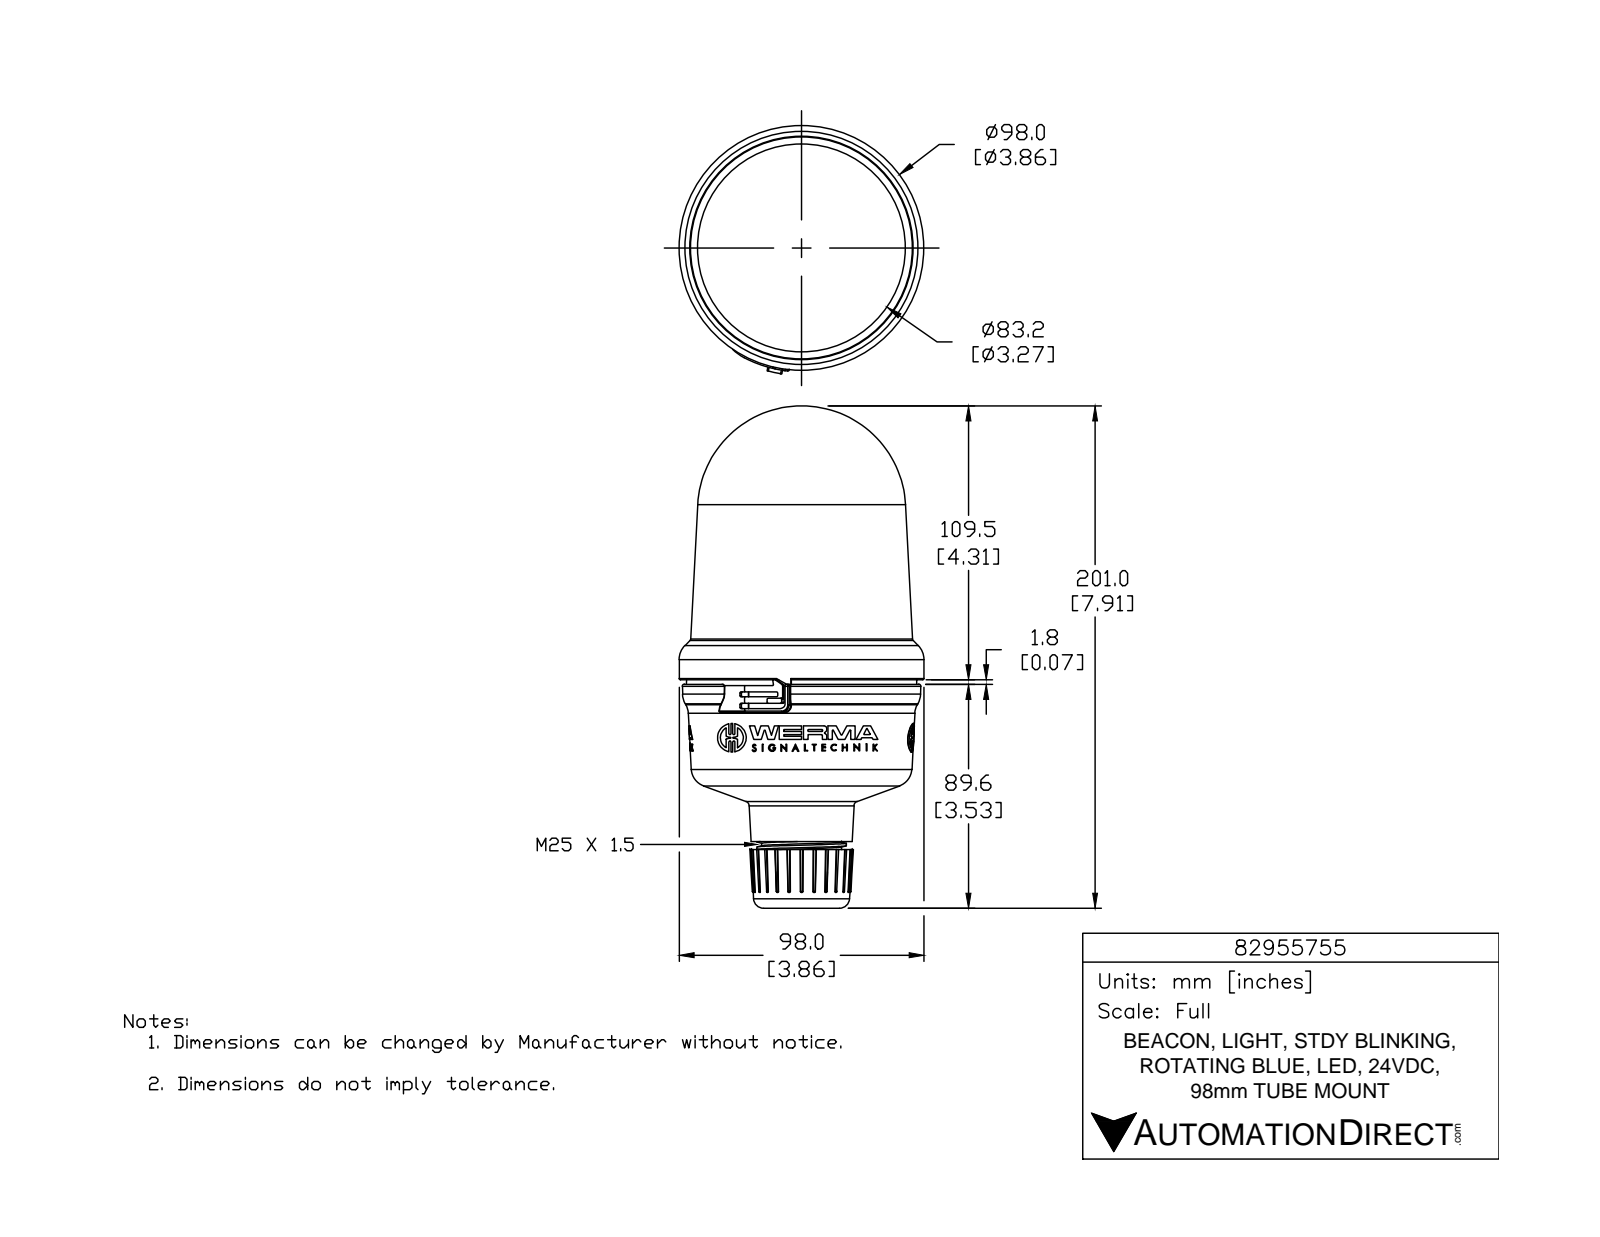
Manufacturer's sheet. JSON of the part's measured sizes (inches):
{"part_name": "82955755", "step_written_by": "SolidWorks 2015 (AUTOMOTIVE_DESIGN)", "units": "inches", "bodies": {"solids": 1, "faces": 1006, "planar": 554, "cylindrical": 189, "other": 263}, "overall_size": [7.914, 3.912, 3.858], "volume_in3": 54.7, "surface_area_in2": 91.39, "round_holes": [[0.078, 3], [1.013, 1], [1.024, 1]], "round_bosses_or_shafts": [[0.452, 3], [0.113, 3], [3.858, 1], [1.409, 1], [1.261, 1]], "partial_cylinders_radius": [[0.02, 12], [0.007, 9], [0.007, 6], [0.016, 6], [0.016, 6], [0.016, 6], [0.262, 6], [0.006, 3]], "face_to_face_distances": [2.214, 0.462, 2.676, 0.335, 0.127, 2.548, 2.603, 2.476, 2.141, 0.073]}
